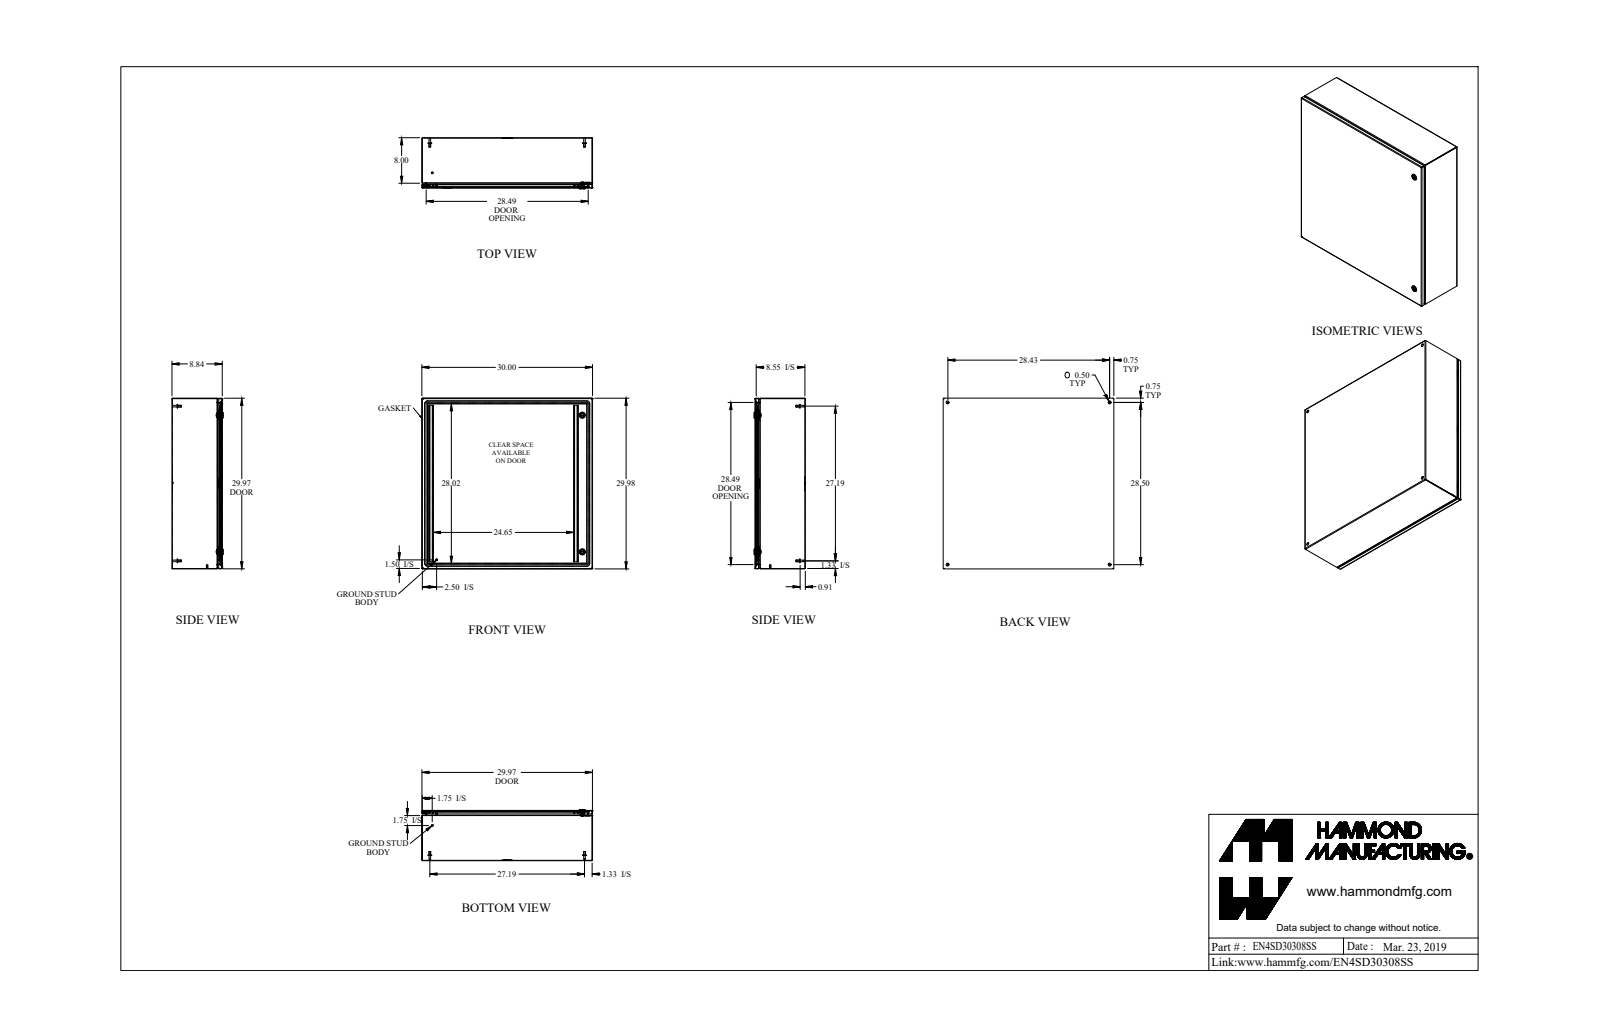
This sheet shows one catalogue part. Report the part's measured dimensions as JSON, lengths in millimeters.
{"part_name": "EN4SD30308SS_Default", "step_written_by": "SolidWorks 2019 (CONFIG_CONTROL_DESIGN)", "units": "millimeters", "bodies": {"solids": 33, "faces": 923, "planar": 450, "cylindrical": 301, "other": 172}, "overall_size": [762, 762, 228.7], "volume_mm3": 3785000, "surface_area_mm2": 4177000, "round_holes": [[12.7, 6], [5, 2], [9.8, 2], [16, 2], [19.5, 2], [4.4, 1], [6.1, 1], [6.1, 1]], "round_bosses_or_shafts": [[15.9, 6], [8, 6], [7, 4], [27.9, 2], [19.9, 2], [13.3, 2], [6.4, 2], [6, 2]], "partial_cylinders_radius": [[0.9, 20], [2.7, 20], [6.4, 16], [0.3, 12], [1.2, 12], [0.2, 6], [1.6, 6], [3.2, 4]], "face_to_face_distances": [1.8, 222.8, 760.2, 220.9, 224.6, 758.3, 762, 21.4, 201.4, 19.1], "hole_center_spacings": [723.9, 63.2, 667.3, 699.3, 964.5, 1023.7, 609.6]}
